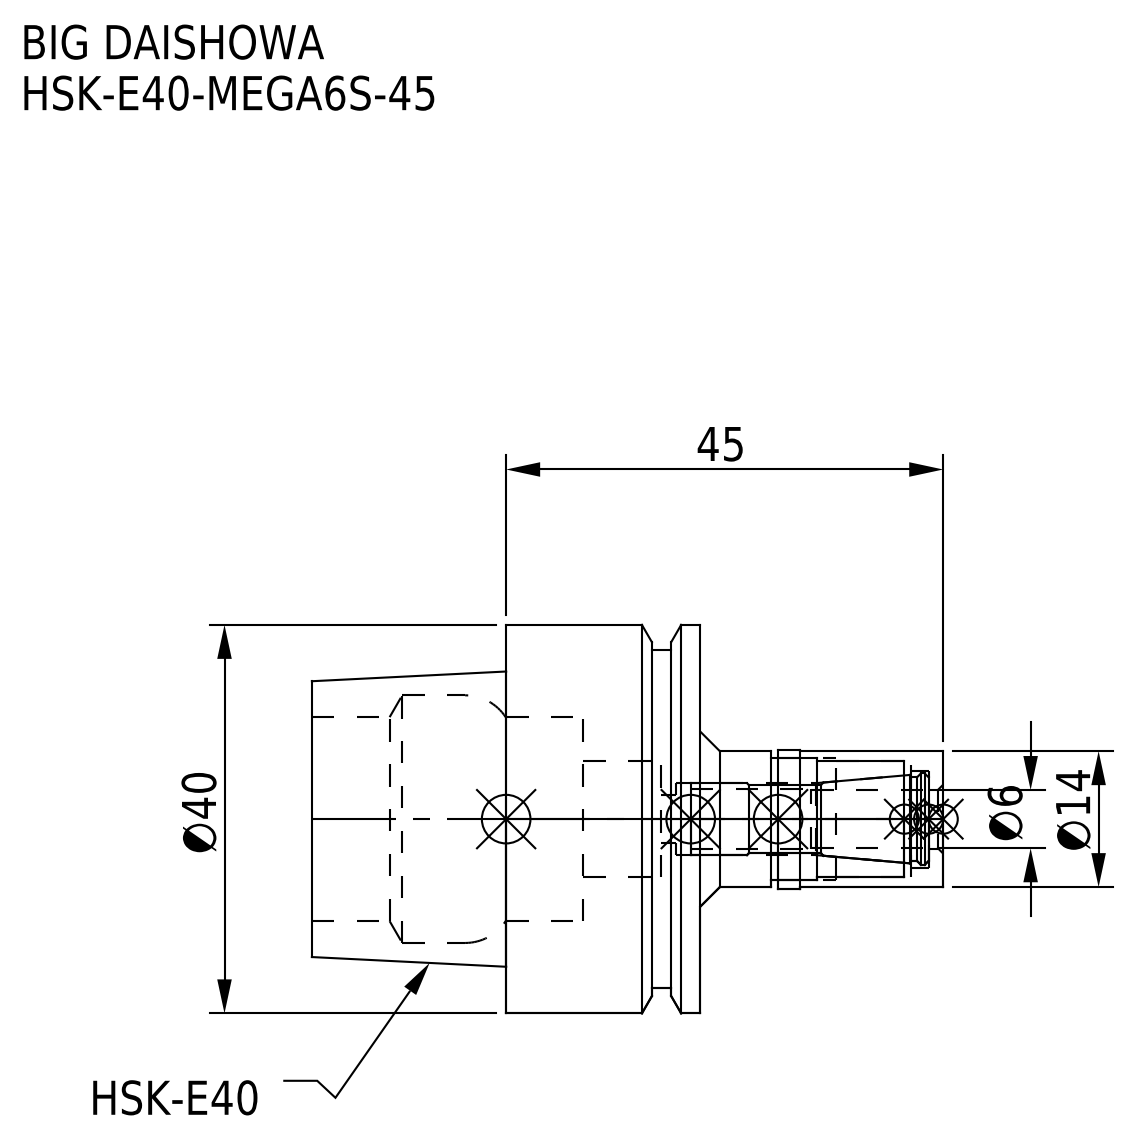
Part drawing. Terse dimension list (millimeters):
name: HSK-E40-MEGA6S-45-060-FreeParts; MGN6S_1.stp; HSK-E40-MEGA6S-45; HSK-E40-MEGA6S-45-060.stp (+3 more)
written by: SolidWorks 2019 (CONFIG_CONTROL_DESIGN)
unit: mm
bodies: 2 solids, 74 faces (18 planar, 40 cylindrical, 16 other)
size: 65 × 40 × 40
volume: 28 177 mm³; area: 12 562 mm²
holes: 1× ⌀4.9, 1× ⌀5, 1× ⌀6.1, 1× ⌀7.4, 1× ⌀10, 1× ⌀12, 1× ⌀12.5, 1× ⌀21, 1× ⌀25.5
bosses: 1× ⌀40, 1× ⌀34.8, 1× ⌀14.3, 1× ⌀14
face distances: 20, 40, 12.05, 7.95, 27.95, 17, 28, 8, 25, 37.05
